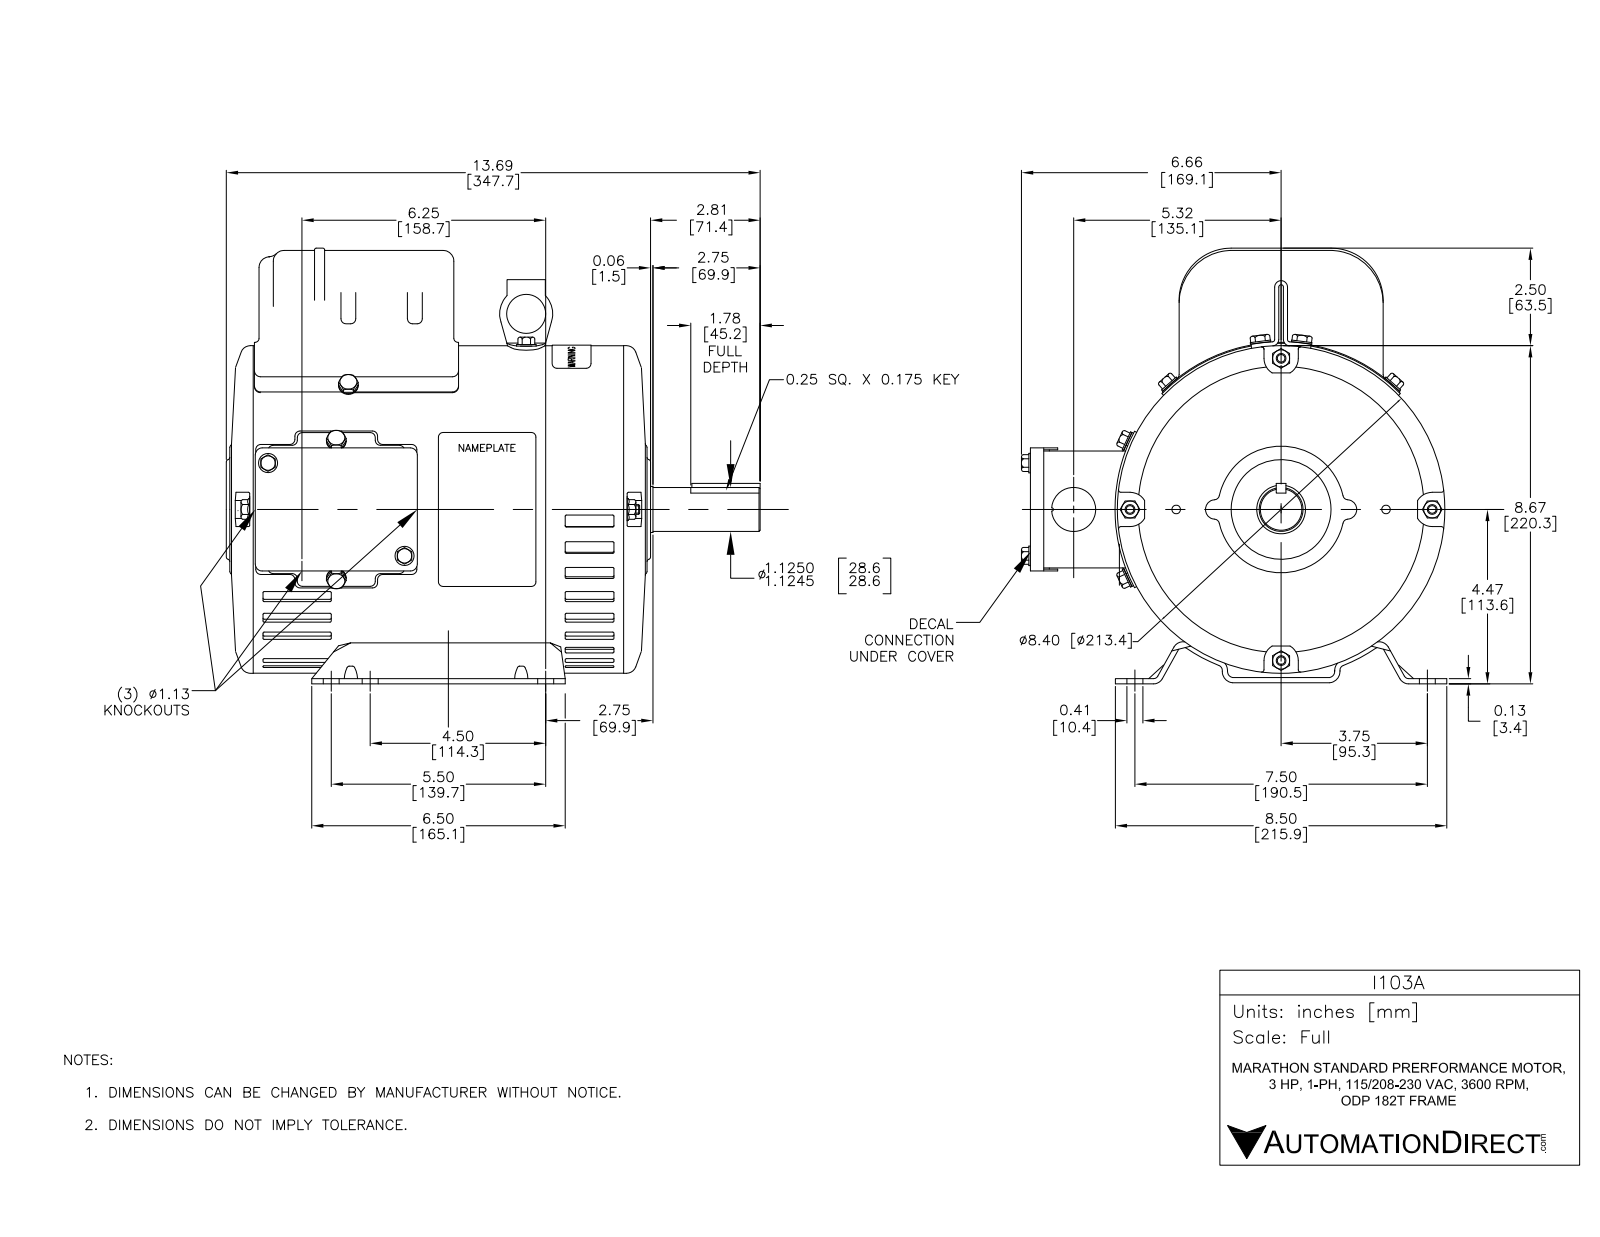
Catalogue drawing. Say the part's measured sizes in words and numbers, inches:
The part is named "035555-950_Rev01". Its 3-D file was written by "SolidWorks 2015 (CONFIG_CONTROL_DESIGN)". It is 38 solids with 4868 faces: 1062 planar, 1001 cylindrical and 2805 other. Overall it measures 13.69 by 11.314 by 10.966 inches. Its volume is 80.27 cubic inches and its surface area 1 495 square inches. Round holes: 9 of diameter 0.213, 8 of diameter 0.38, 6 of diameter 0.266, 6 of diameter 0.43, 4 of diameter 0.25, 4 of diameter 0.28, 2 of diameter 0.103, 2 of diameter 0.5, 2 of diameter 1.125, 1 of diameter 1, 1 of diameter 1.181, 1 of diameter 1.25. Round bosses or shafts: 12 of diameter 0.52, 8 of diameter 0.25, 4 of diameter 0.609, 2 of diameter 0.309, 2 of diameter 0.112, 1 of diameter 8.181, 1 of diameter 2.441, 1 of diameter 1.871. Partial cylindrical surfaces (rounded edges, fillets, slot ends): 182 of radius 0.03, 87 of radius 0.045, 59 of radius 0.06, 37 of radius 0.13, 22 of radius 0.01, 22 of radius 0.036, 10 of radius 0.25, 8 of radius 0.264. The main face-to-face distances are 0.026, 0.048, 0.13, 0.134, 0.178, 5.206, 3, 2.952, 0.134, 0.03. The hole center spacings are 5.48, 1.5, 3, 3.875, 4.5, 5.48, 3.875, 6.576.
